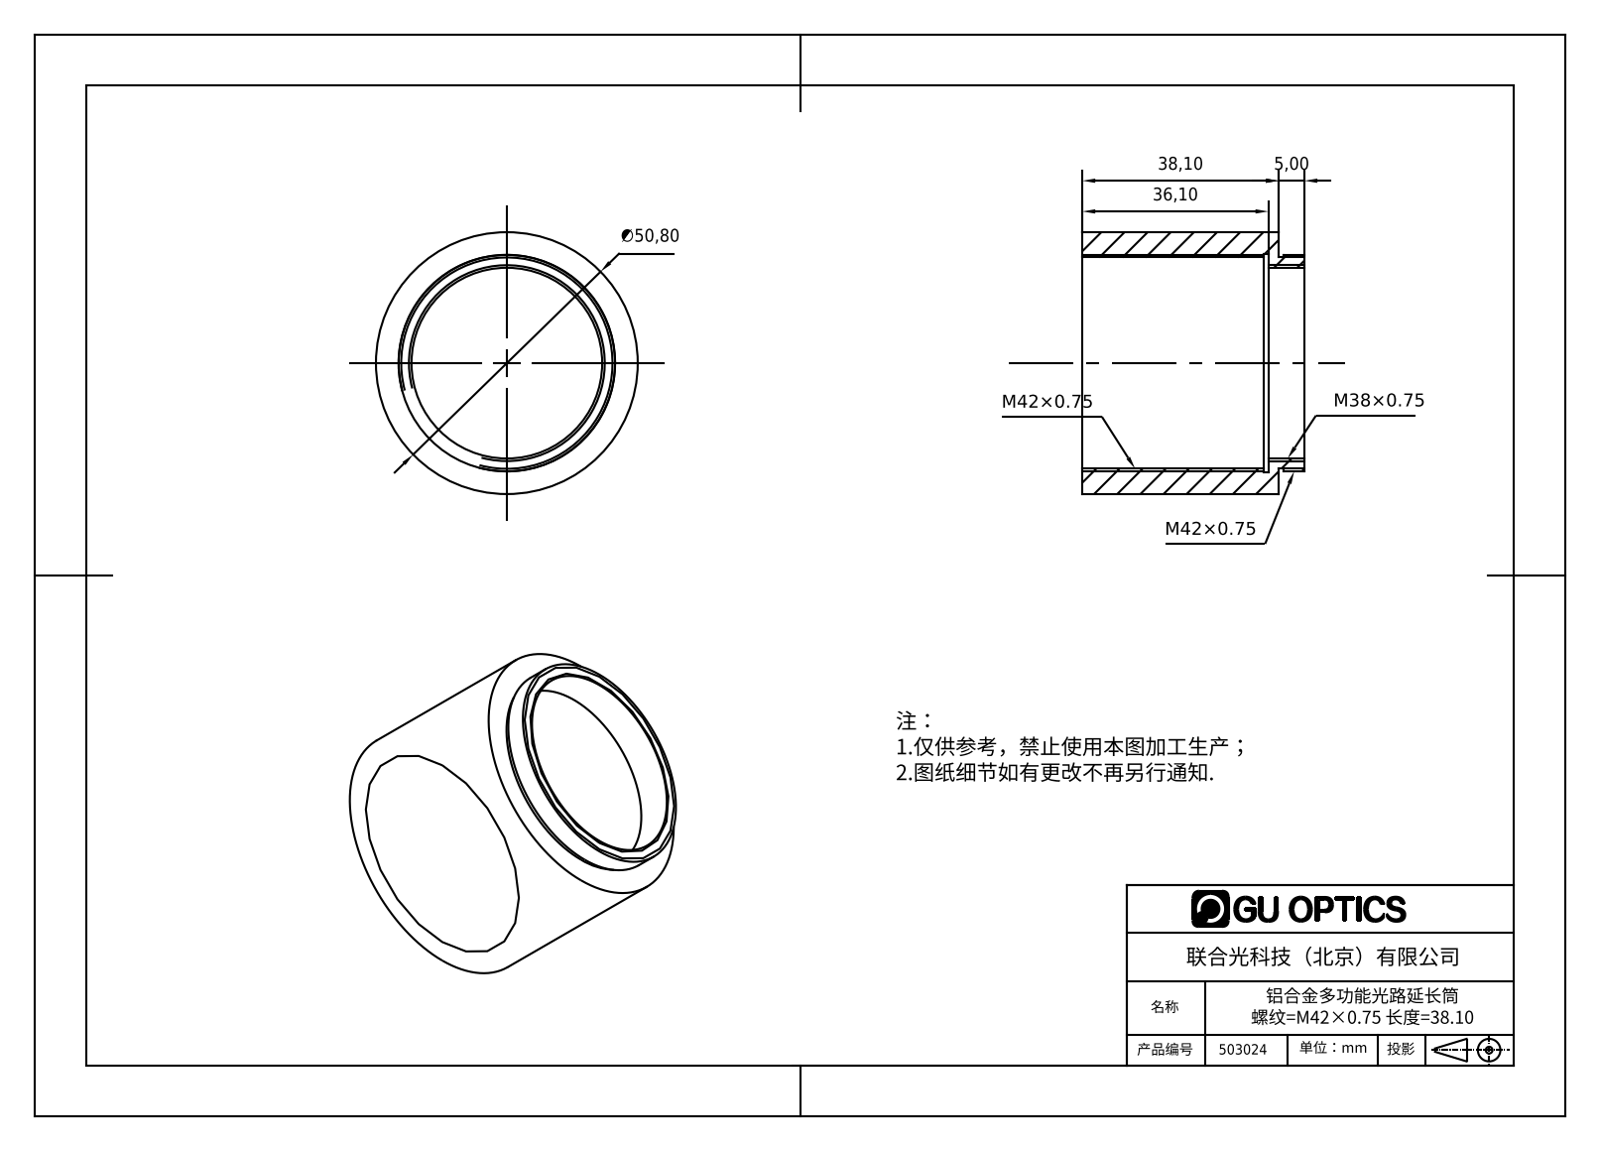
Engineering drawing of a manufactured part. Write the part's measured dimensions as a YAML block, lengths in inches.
part_name: "503024"
step_written_by: "SolidWorks 2016 (AUTOMOTIVE_DESIGN)"
units: inches
bodies: {solids: 1, faces: 18, planar: 6, cylindrical: 12, other: 0}
overall_size: [2, 2, 1.697]
volume: 1.759
surface_area: 22.31
round_holes:
  - {diameter: 1.457, count: 1}
  - {diameter: 1.614, count: 1}
  - {diameter: 1.661, count: 1}
round_bosses_or_shafts:
  - {diameter: 2, count: 1}
  - {diameter: 1.654, count: 1}
face_to_face_distances: [1.5, 1.421, 0.079, 1.697, 0.276, 0.197, 0.039, 0.118, 0.157, 1.382]
